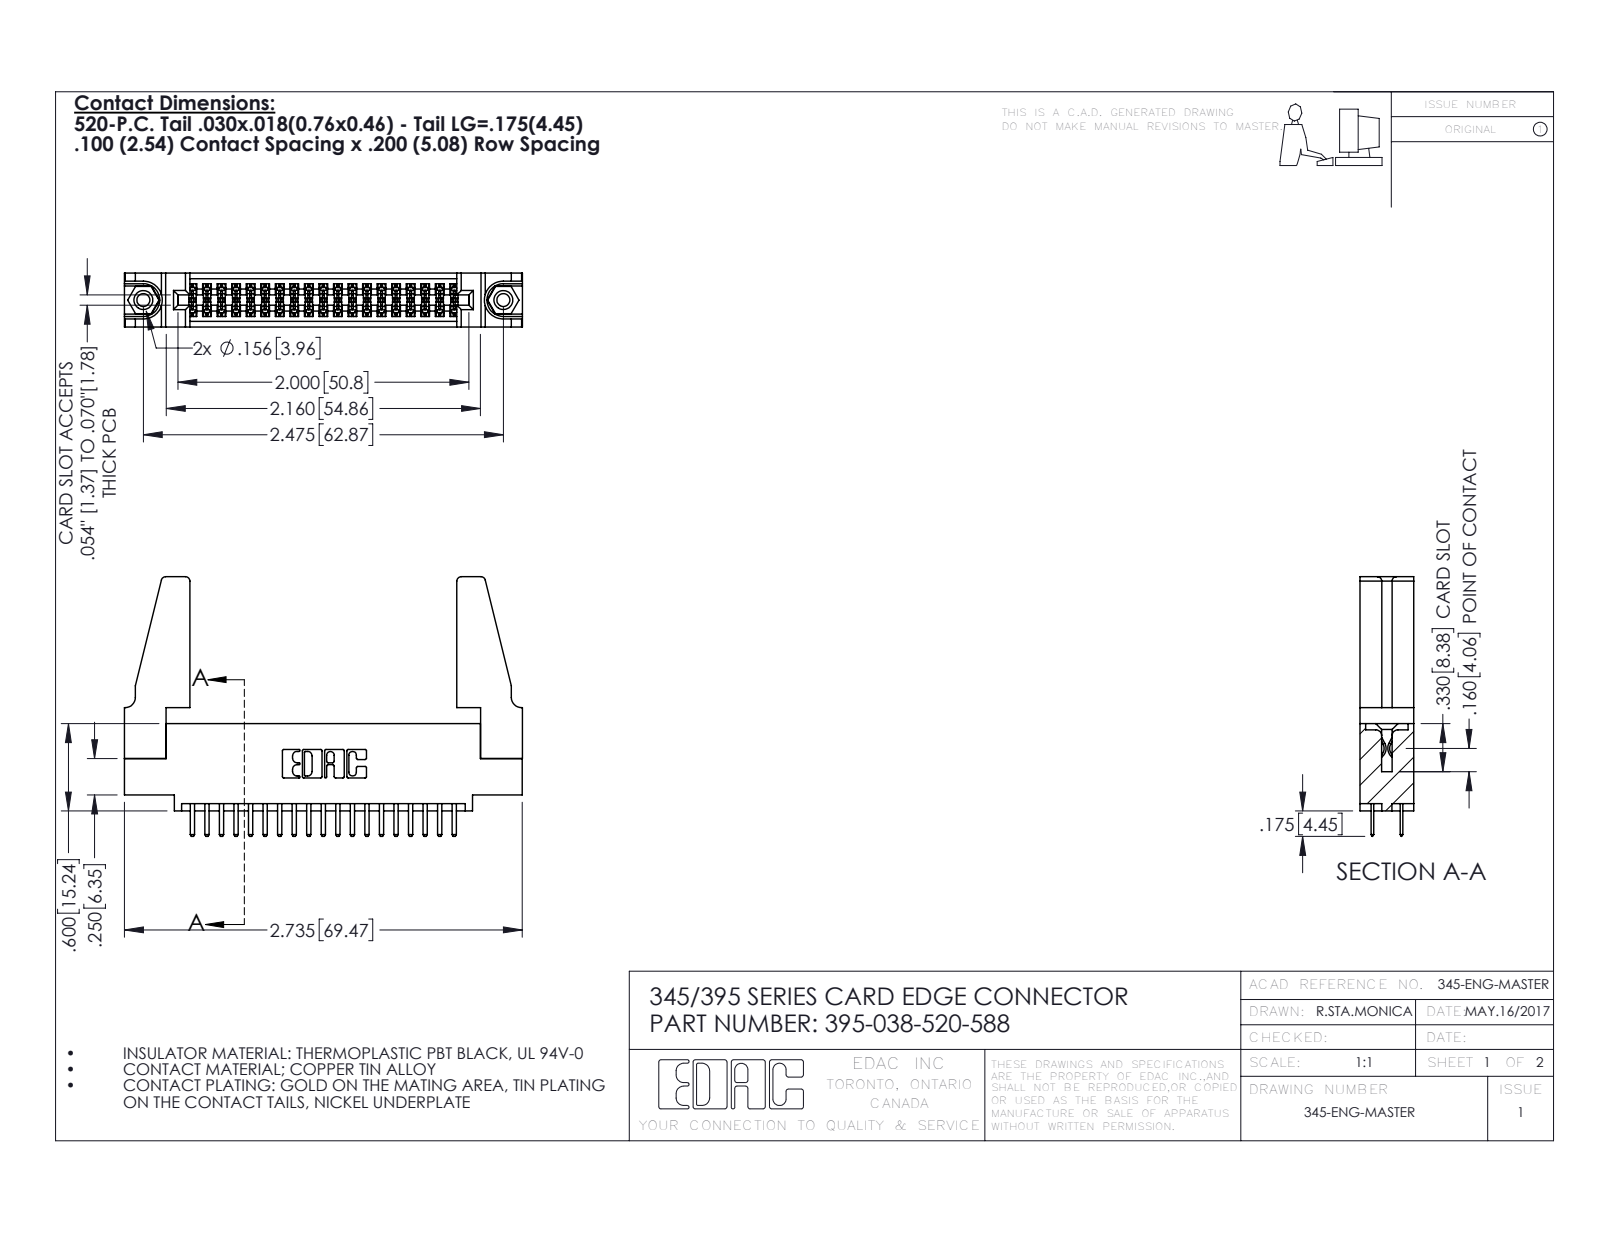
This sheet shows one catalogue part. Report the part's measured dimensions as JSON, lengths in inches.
{"part_name": "345-220-078_345-220-088; 345-250-001_345-250-001-102; 395-038-520-588; 345 Part_0.110 Offset - 0.156 Dia-TH (+1 more)", "step_written_by": "SolidWorks 2016 (CONFIG_CONTROL_DESIGN)", "units": "inches", "bodies": {"solids": 43, "faces": 2306, "planar": 1486, "cylindrical": 804, "other": 16}, "overall_size": [2.736, 1.785, 0.37], "volume_in3": 0.592, "surface_area_in2": 19.01, "round_holes": [[0.089, 2], [0.125, 2], [0.156, 2], [0.064, 1]], "round_bosses_or_shafts": [[0.155, 2]], "partial_cylinders_radius": [[0.006, 57], [0.01, 42], [0.01, 22], [0.03, 8], [0.007, 6], [0.031, 6], [0.026, 3], [0.014, 2]], "face_to_face_distances": [0.37, 0.072, 0.298, 0.2, 0.098, 0.272, 0.025, 0.225, 0.072, 0.022], "hole_center_spacings": [0.27, 2.241, 2.475]}
